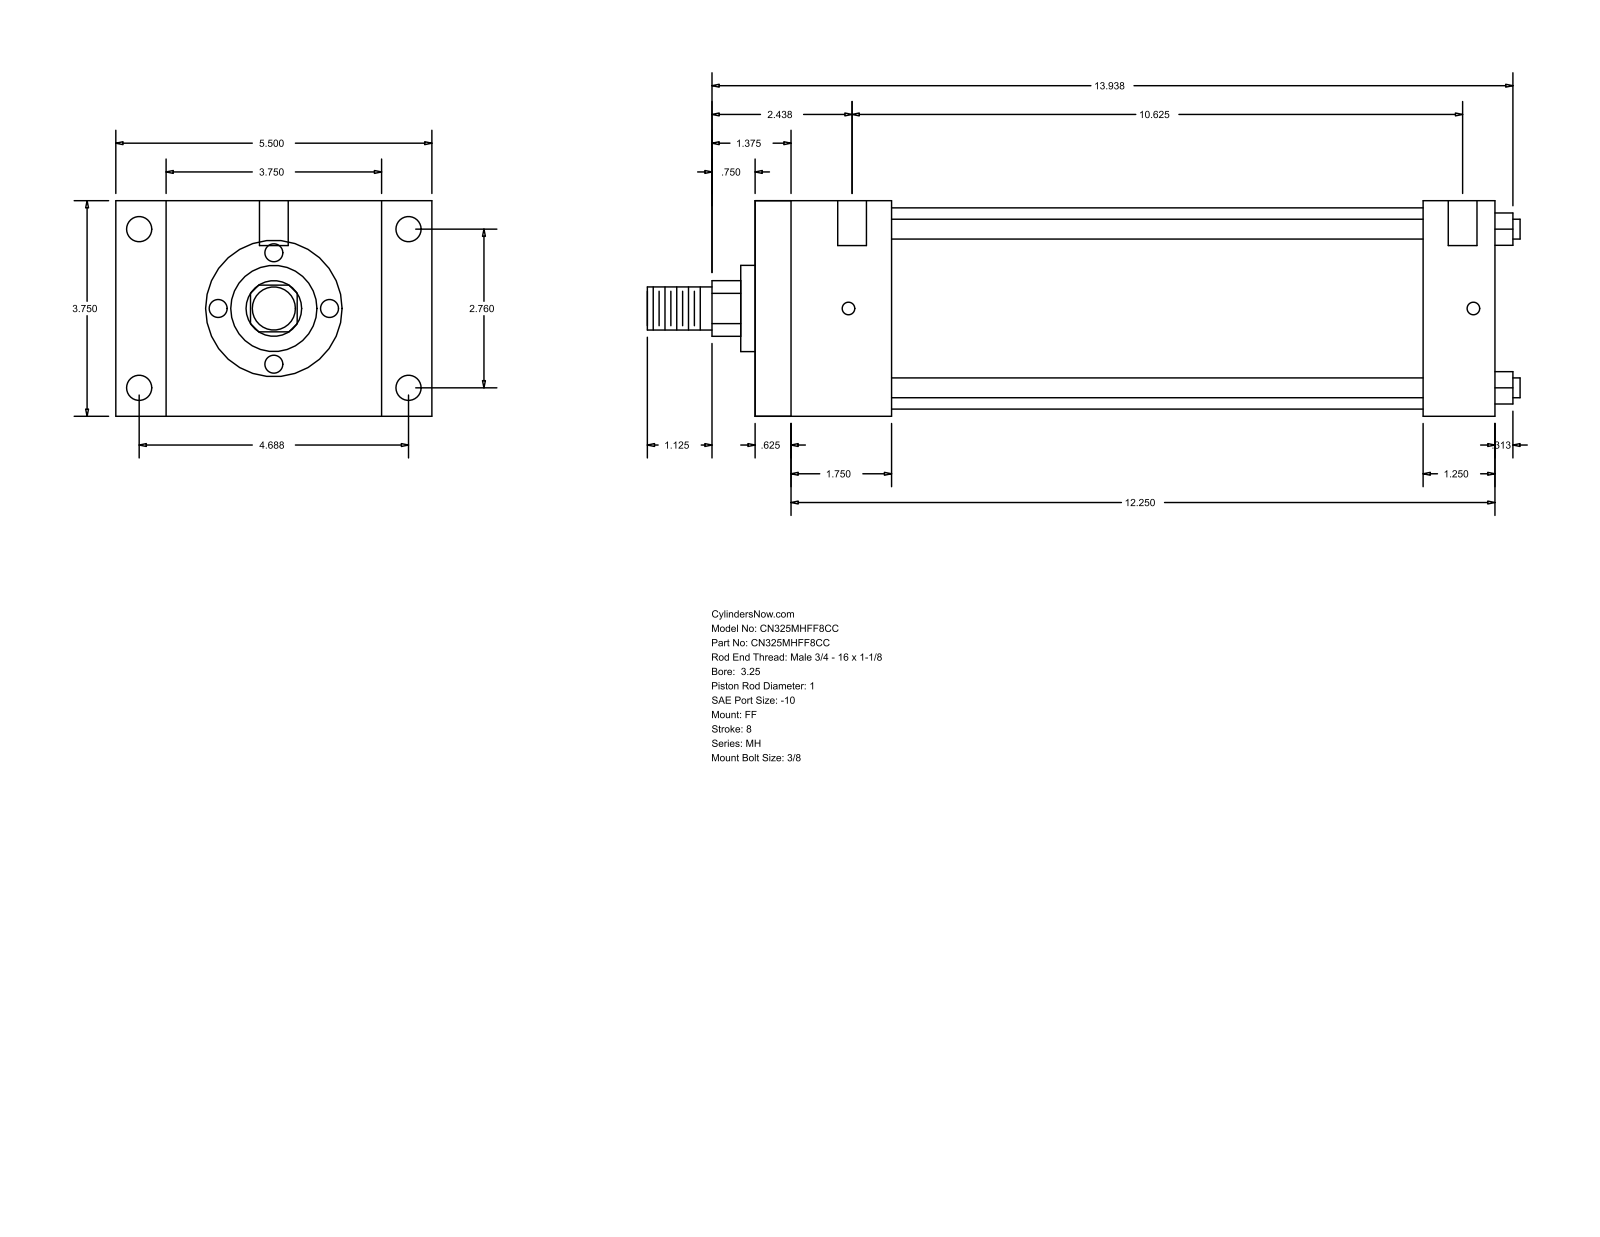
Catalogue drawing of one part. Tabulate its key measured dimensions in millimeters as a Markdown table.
| quantity | value |
| --- | --- |
| part name | MH_FF__0325_1 |
| STEP written by | GSSL Pune (CONFIG_CONTROL_DESIGN) |
| units | millimeters |
| bodies | 0 solids, 92 faces (64 planar, 28 cylindrical, 0 other) |
| overall size | 385.76 × 139.7 × 95.25 |
| round holes (diameter × count) | 5.56 × 4, 11.13 × 4, 12.7 × 2 |
| round bosses / shafts (diameter × count) | 8.76 × 4, 88.9 × 1, 38.1 × 1, 25.4 × 1, 19.05 × 1 |
| partial cylindrical surfaces (radius × count) | 12.29 × 1 |
| main face-to-face distances | 95.24, 327.02, 15.87, 311.15, 22.23, 117.47, 295.27, 279.4, 31.75, 60.33 |
| hole center spacings | 70.1, 119.06, 138.16, 276.22, 1.58, 4.76, 269.88, 271.46 |
